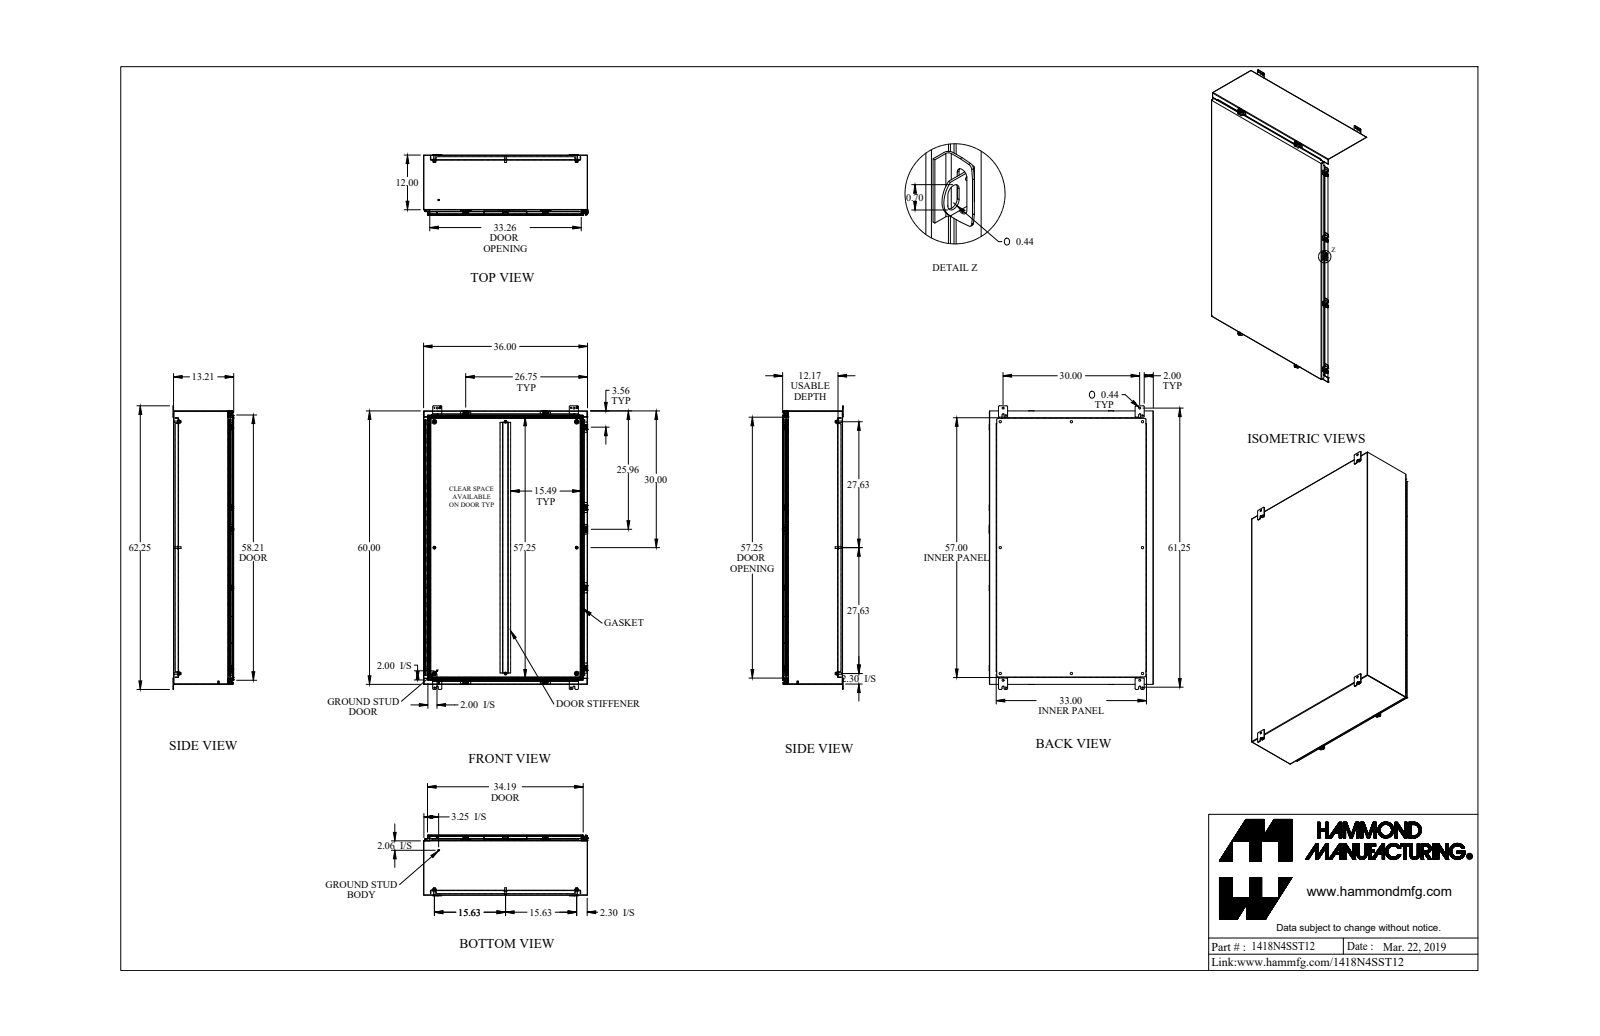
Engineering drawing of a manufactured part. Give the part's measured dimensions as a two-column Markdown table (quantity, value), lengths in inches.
| quantity | value |
| --- | --- |
| part name | 1418N4SST12_Default |
| STEP written by | SolidWorks 2019 (CONFIG_CONTROL_DESIGN) |
| units | inches |
| bodies | 66 solids, 2432 faces (1459 planar, 889 cylindrical, 84 other) |
| overall size | 62.25 × 36.063 × 13.375 |
| volume | 742.6 in³ |
| surface area | 19 375 in² |
| round holes (diameter × count) | 0.213 × 8, 0.265 × 8, 0.375 × 8, 0.5 × 8, 0.307 × 4, 0.313 × 4, 0.437 × 4, 0.445 × 4, 0.125 × 1, 0.187 × 1 |
| round bosses / shafts (diameter × count) | 0.65 × 8, 0.5 × 8, 0.39 × 8, 0.375 × 8, 0.332 × 8, 0.244 × 8, 1 × 4, 0.313 × 2 |
| partial cylindrical surfaces (radius × count) | 0.25 × 44, 0.048 × 39, 0.143 × 39, 0.188 × 30, 0.036 × 22, 0.108 × 22, 0.141 × 16, 0.125 × 12 |
| main face-to-face distances | 0.072, 13.066, 13.138, 0.072, 0.095, 13.138, 13.21, 0.937, 1.009, 12.106 |
| hole center spacings | 31.25, 9.004, 27.625, 30, 41.709, 62.338, 63.475, 1.736 |
